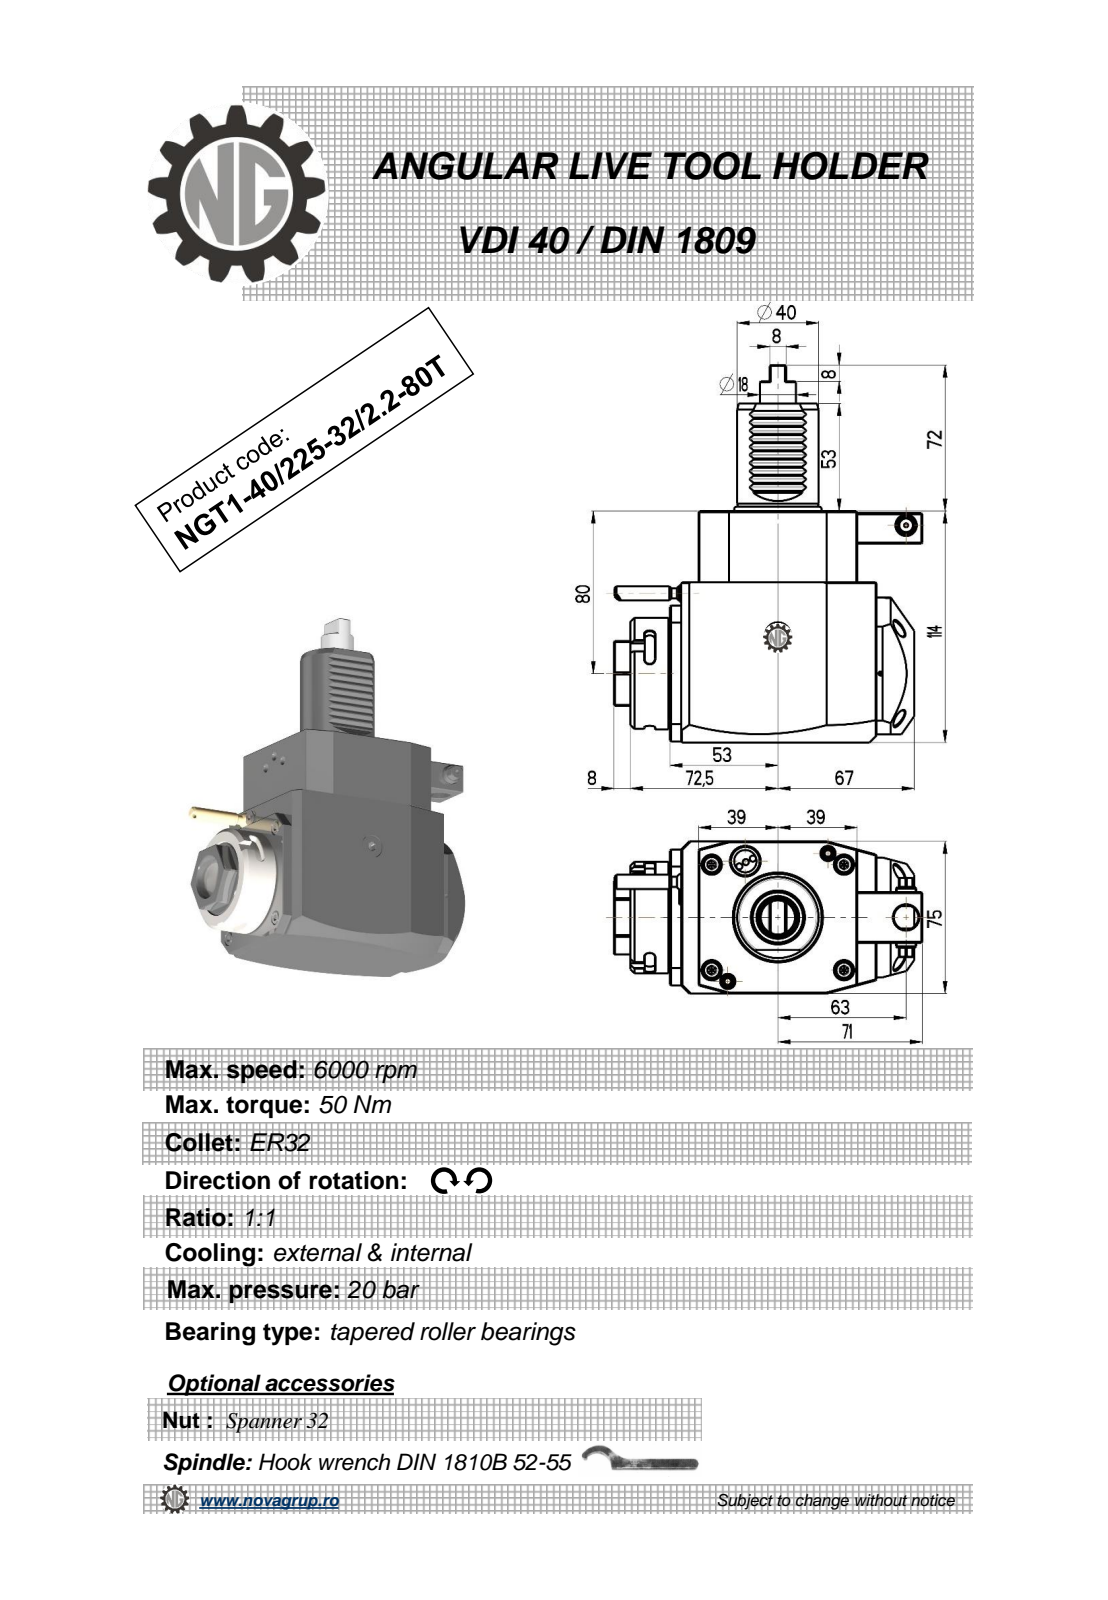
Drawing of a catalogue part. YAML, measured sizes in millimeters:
part_name: "NGT1_40_225_32_1_2_80T"
step_written_by: "PRO/ENGINEER BY PARAMETRIC TECHNOLOGY CORPORATION, 2010280 (CONFIG_CONTROL_DESIGN)"
units: millimeters
bodies: {solids: 1, faces: 344, planar: 192, cylindrical: 80, other: 72}
overall_size: [186, 151.5, 75]
volume: 955161
surface_area: 71409
round_holes:
  - {diameter: 2, count: 1}
  - {diameter: 2.5, count: 1}
  - {diameter: 3, count: 1}
  - {diameter: 9.5, count: 1}
  - {diameter: 12, count: 1}
  - {diameter: 23, count: 1}
round_bosses_or_shafts:
  - {diameter: 8, count: 2}
  - {diameter: 55, count: 1}
  - {diameter: 48, count: 1}
  - {diameter: 40, count: 1}
  - {diameter: 17.8, count: 1}
  - {diameter: 10, count: 1}
  - {diameter: 7, count: 1}
  - {diameter: 5, count: 1}
partial_cylinders:
  - {radius: 0.3, count: 10}
  - {radius: 2.5, count: 6}
  - {radius: 0.8, count: 2}
  - {radius: 180, count: 2}
  - {radius: 0.5, count: 1}
  - {radius: 3.85, count: 1}
  - {radius: 4.25, count: 1}
  - {radius: 24.5, count: 1}
face_to_face_distances: [75, 114, 14, 92, 78, 25, 19.5, 33.5, 111.5, 35]
hole_center_spacings: [37.35, 43.2, 72.5]
